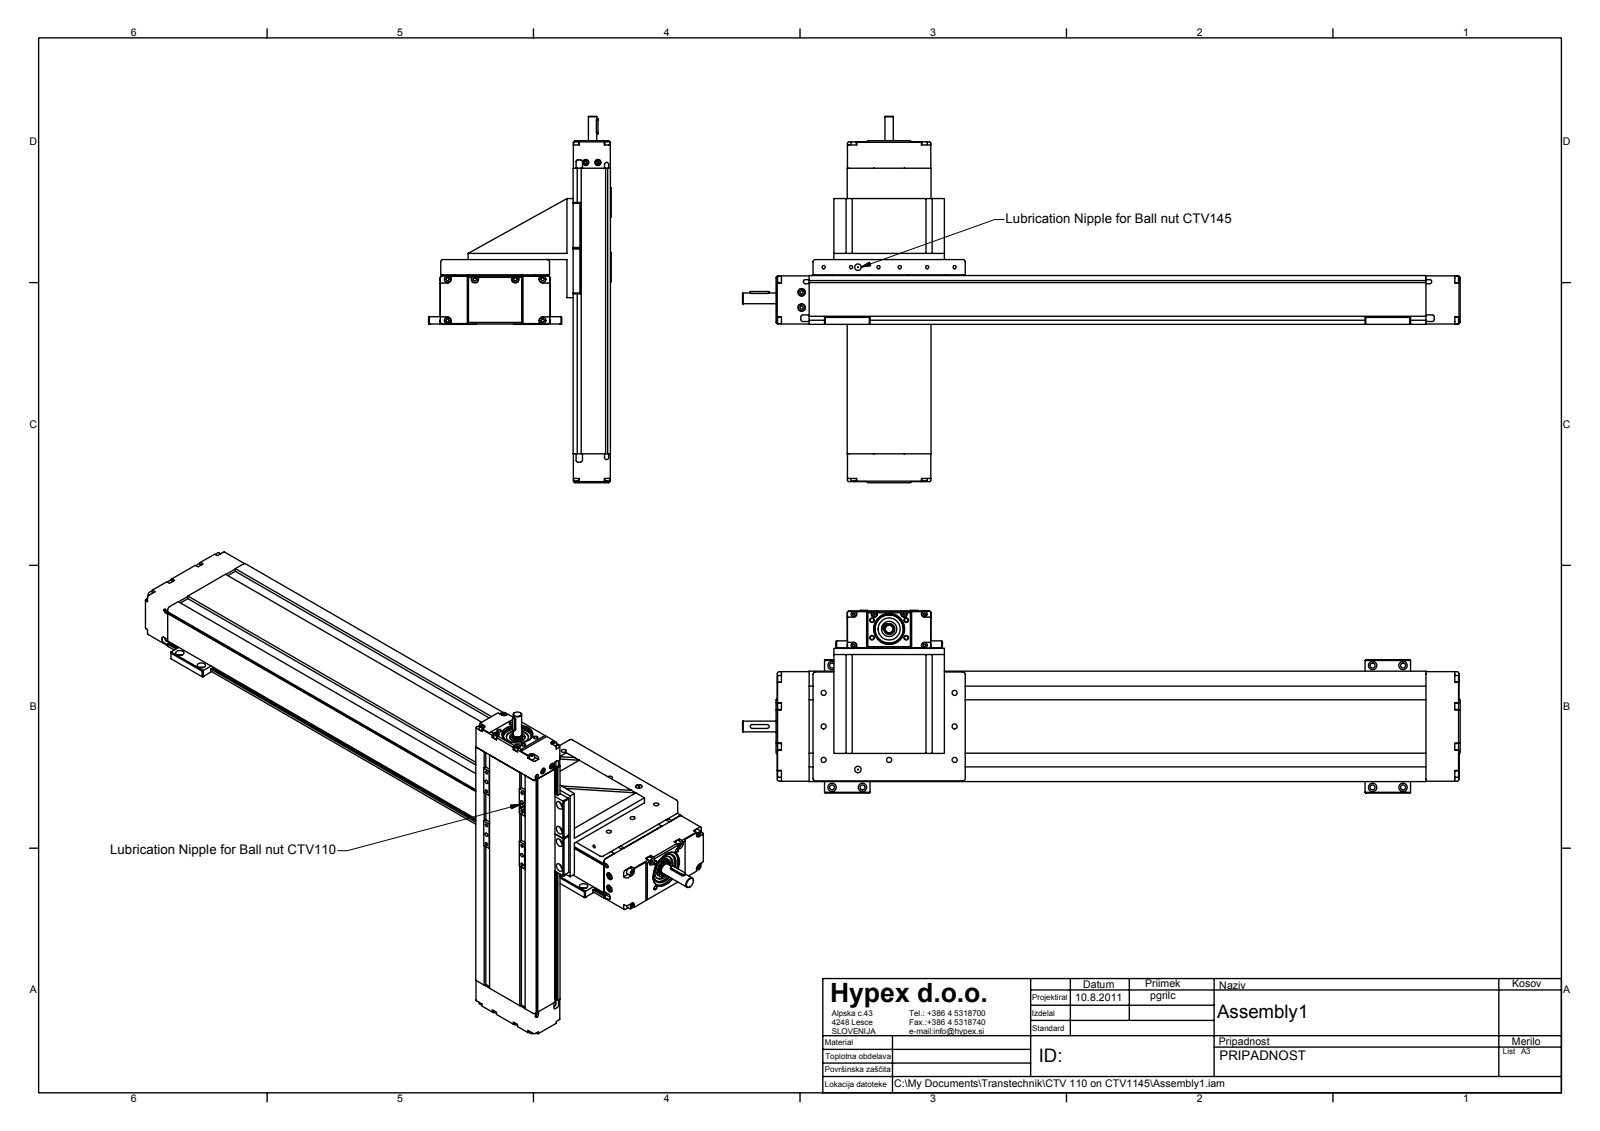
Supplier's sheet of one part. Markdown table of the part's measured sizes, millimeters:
| quantity | value |
| --- | --- |
| part name | CTV 145 L IPART-021; CTV 110 L IPART-01; CP C110 0 ZC110 90; PRITRDILNA SPONA CTV 110 IN CTV 145 |
| STEP written by | Autodesk Inventor 2012 (AUTOMOTIVE_DESIGN) |
| units | millimeters |
| bodies | 7 solids, 1180 faces (783 planar, 265 cylindrical, 132 other) |
| overall size | 942.5 × 481 × 207 |
| volume | 11 350 000 mm³ |
| surface area | 836 480 mm² |
| round holes (diameter × count) | 4.92 × 16, 4.13 × 14, 6.65 × 9, 6.5 × 8, 11 × 8, 9 × 6, 1.7 × 4, 5 × 4, 6 × 4, 8.5 × 4, 4.2 × 2, 8 × 2 |
| round bosses / shafts (diameter × count) | 8.5 × 8, 7 × 8, 1 × 4, 4 × 2, 24.36 × 1, 20 × 1, 19.77 × 1, 17 × 1 |
| partial cylindrical surfaces (radius × count) | 2.5 × 18, 3 × 16, 2 × 10, 0.91 × 8, 4 × 6, 4.75 × 6, 2.25 × 4, 2.55 × 4 |
| main face-to-face distances | 64, 1, 0.5, 63, 157, 85, 21, 8, 145, 12 |
| hole center spacings | 100, 18, 36, 89.82, 88, 15, 25.1, 40 |
